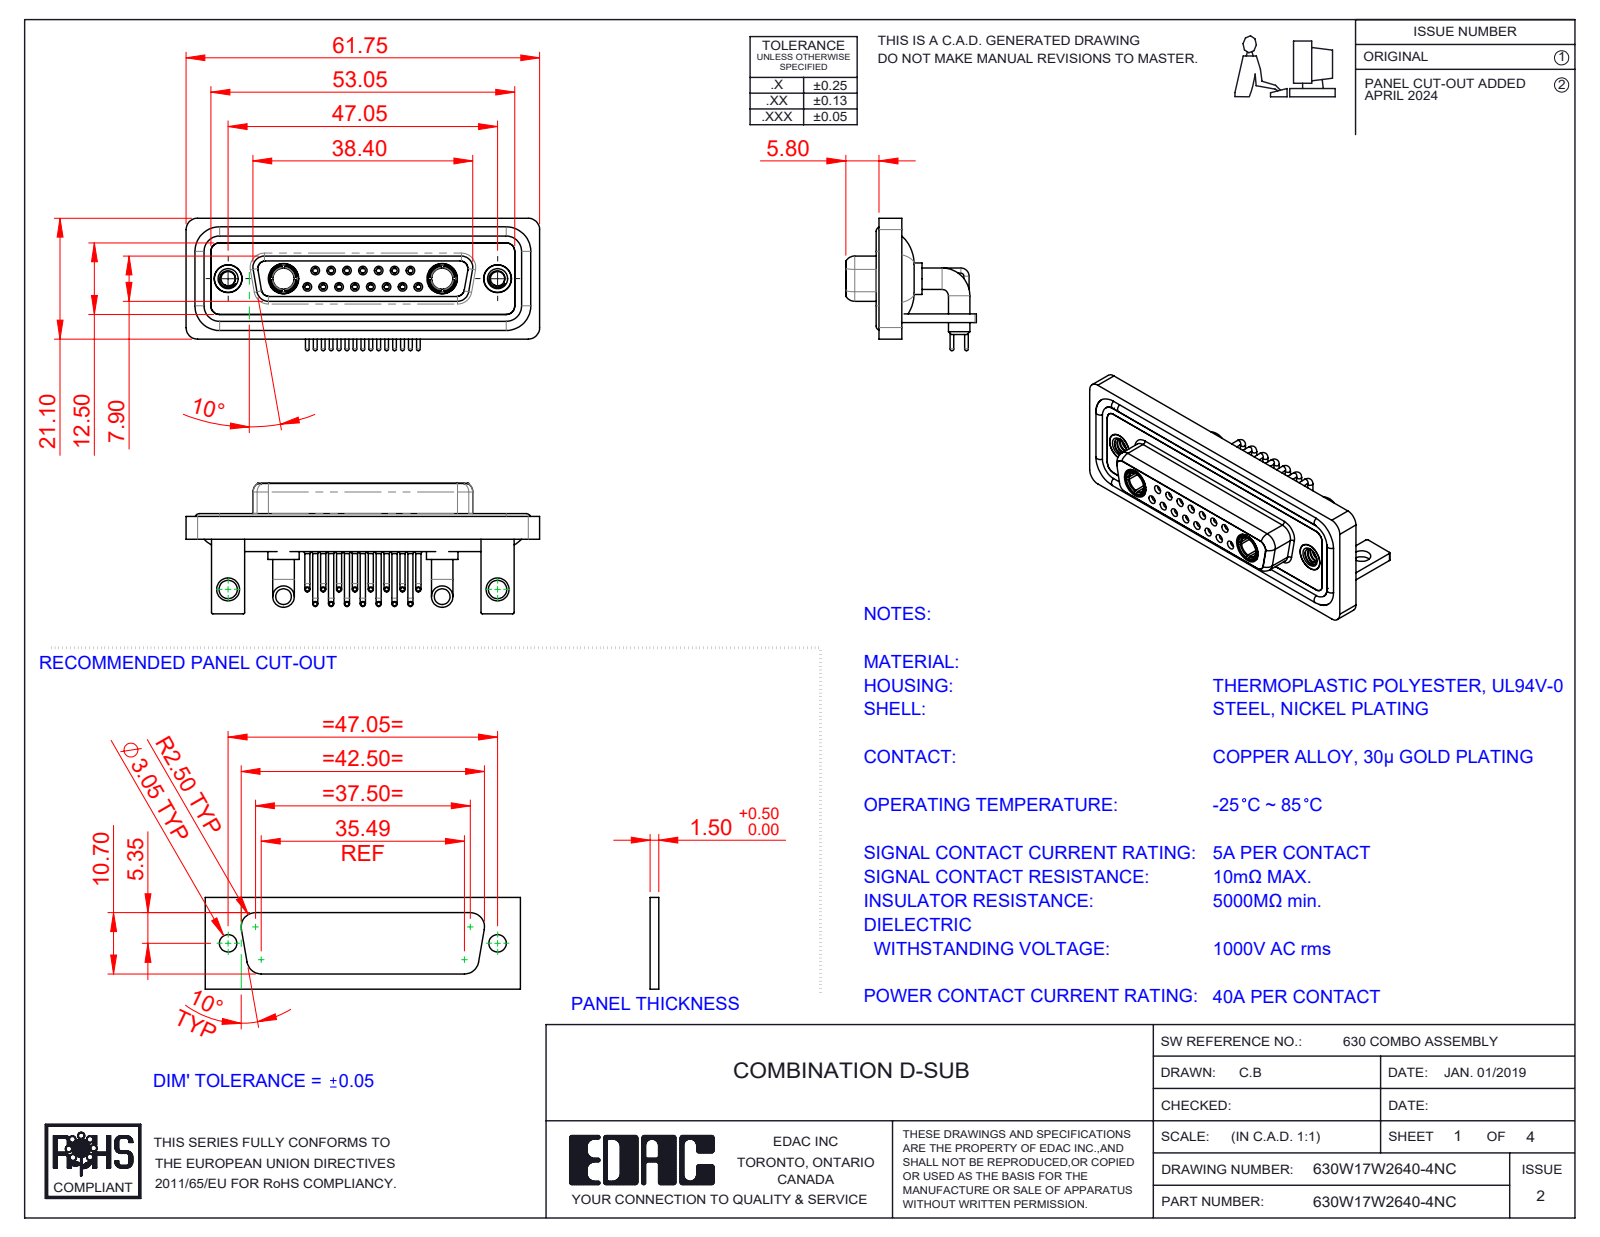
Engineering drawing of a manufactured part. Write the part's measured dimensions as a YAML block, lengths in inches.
part_name: "630Combo Shell Front_25 Contacts; 630Combo Housing_17W2; 630Combo Stabilizer Bracket_50 Contacts; 630Combo Shell Rear_25 Contacts (+6 more)"
step_written_by: "SolidWorks 2023 (CONFIG_CONTROL_DESIGN)"
units: inches
bodies: {solids: 28, faces: 1379, planar: 408, cylindrical: 605, other: 366}
overall_size: [2.431, 0.91, 0.898]
volume: 0.549
surface_area: 23.8
round_holes:
  - {diameter: 0.035, count: 15}
  - {diameter: 0.043, count: 15}
  - {diameter: 0.059, count: 15}
  - {diameter: 0.079, count: 15}
  - {diameter: 0.063, count: 8}
  - {diameter: 0.067, count: 7}
  - {diameter: 0.191, count: 4}
  - {diameter: 0.098, count: 2}
  - {diameter: 0.126, count: 2}
  - {diameter: 0.146, count: 2}
  - {diameter: 0.157, count: 2}
  - {diameter: 0.159, count: 2}
round_bosses_or_shafts:
  - {diameter: 0.035, count: 15}
  - {diameter: 0.026, count: 15}
  - {diameter: 0.063, count: 11}
  - {diameter: 0.148, count: 4}
  - {diameter: 0.217, count: 2}
  - {diameter: 0.205, count: 2}
  - {diameter: 0.195, count: 2}
  - {diameter: 0.195, count: 2}
partial_cylinders:
  - {radius: 0.079, count: 19}
  - {radius: 0.059, count: 18}
  - {radius: 0.01, count: 16}
  - {radius: 0.053, count: 8}
  - {radius: 0.063, count: 8}
  - {radius: 0.02, count: 5}
  - {radius: 0.024, count: 4}
  - {radius: 0.026, count: 4}
face_to_face_distances: [0.016, 0.071, 0.114, 0.146, 0.059, 0.161, 0.043, 0.055, 0.063, 0.122]
hole_center_spacings: [0.124, 0.109, 0.218, 0.327, 0.198, 0.295, 0.436, 0.198]
